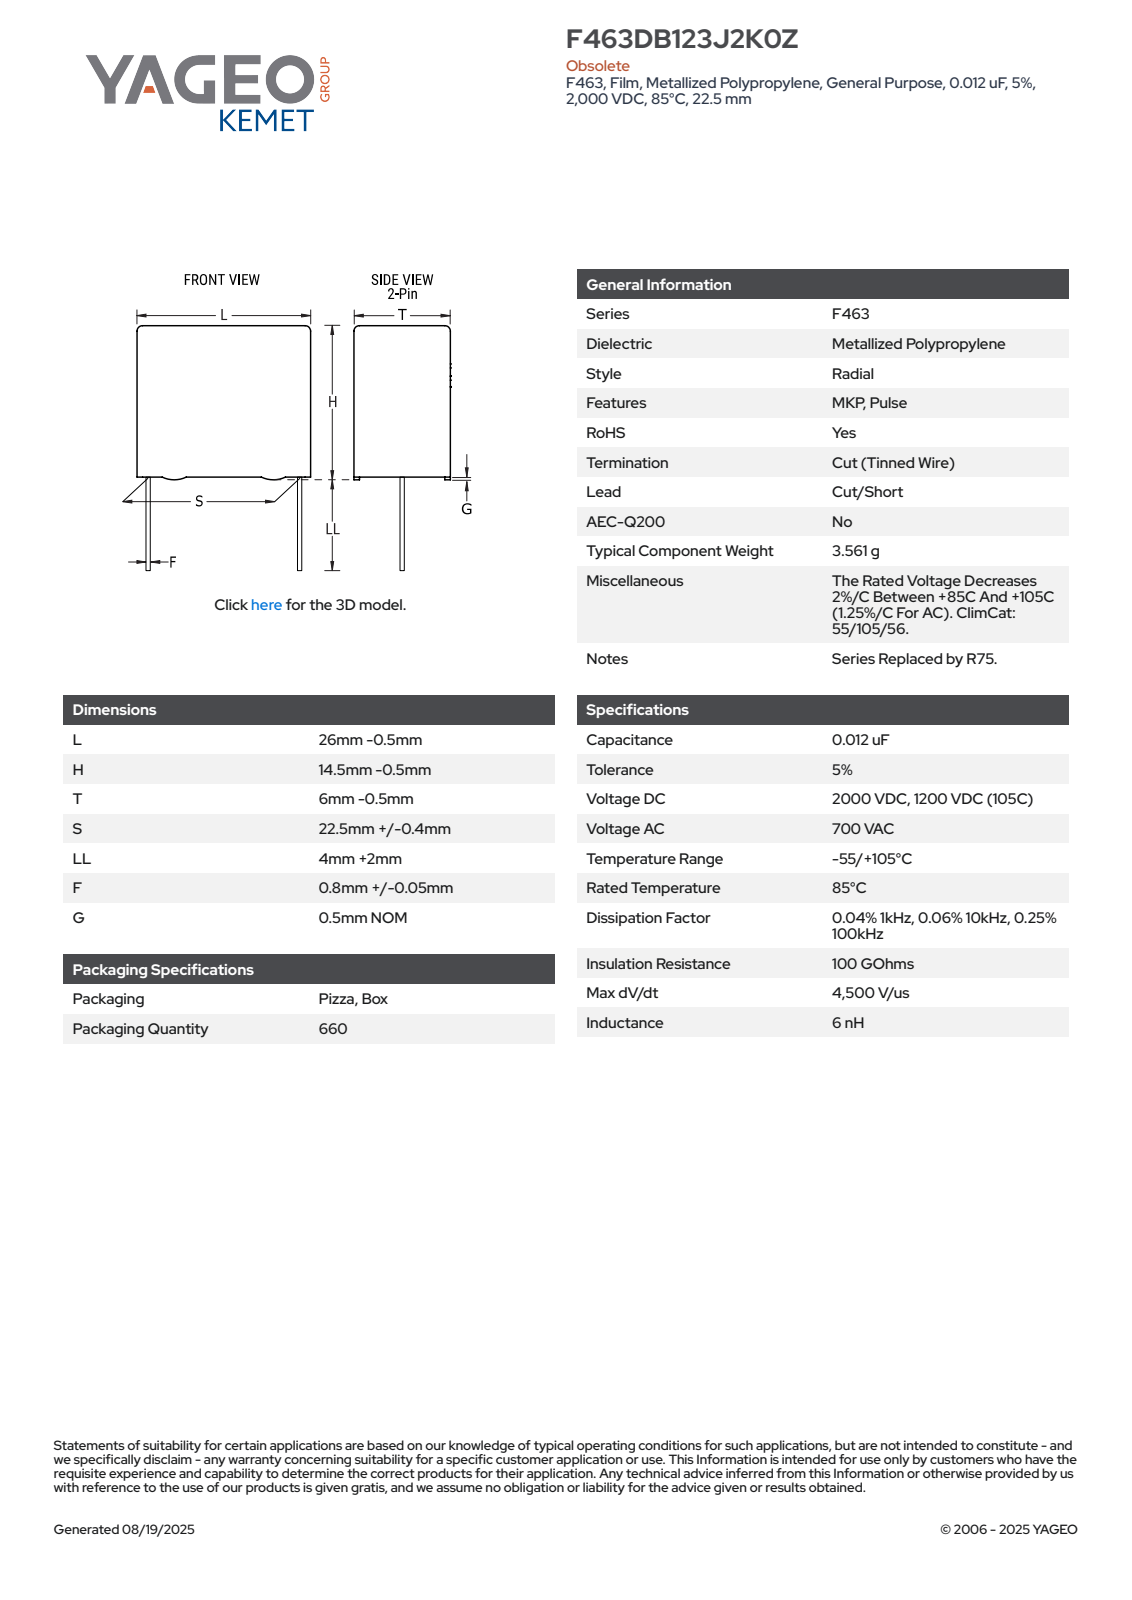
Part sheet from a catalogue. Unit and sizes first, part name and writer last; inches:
Units: inches
Overall size (bounding box): 1.004 × 0.787 × 0.217
Round bosses / shafts (diameter × count): ⌀0.033 ×2
Partial cylindrical surfaces — rounded edges, fillets, slot ends (radius × count): R0.02 ×4
Main face-to-face distances: 0.217, 0.531, 1.004, 0.012, 0.204, 0.02, 0.551, 0.192, 0.236, 0.256
Volume: 0.116 in³ · Surface area: 1.9 in²
Bodies: 4 solids, 89 faces (81 planar, 8 cylindrical, 0 other)
Part name (STEP PRODUCT): CFR_RBG_26X14.5X6_L25.5H14T5.5S22.5LL6F0.85G0.5
STEP written by: SolidWorks 2014 (AUTOMOTIVE_DESIGN)
